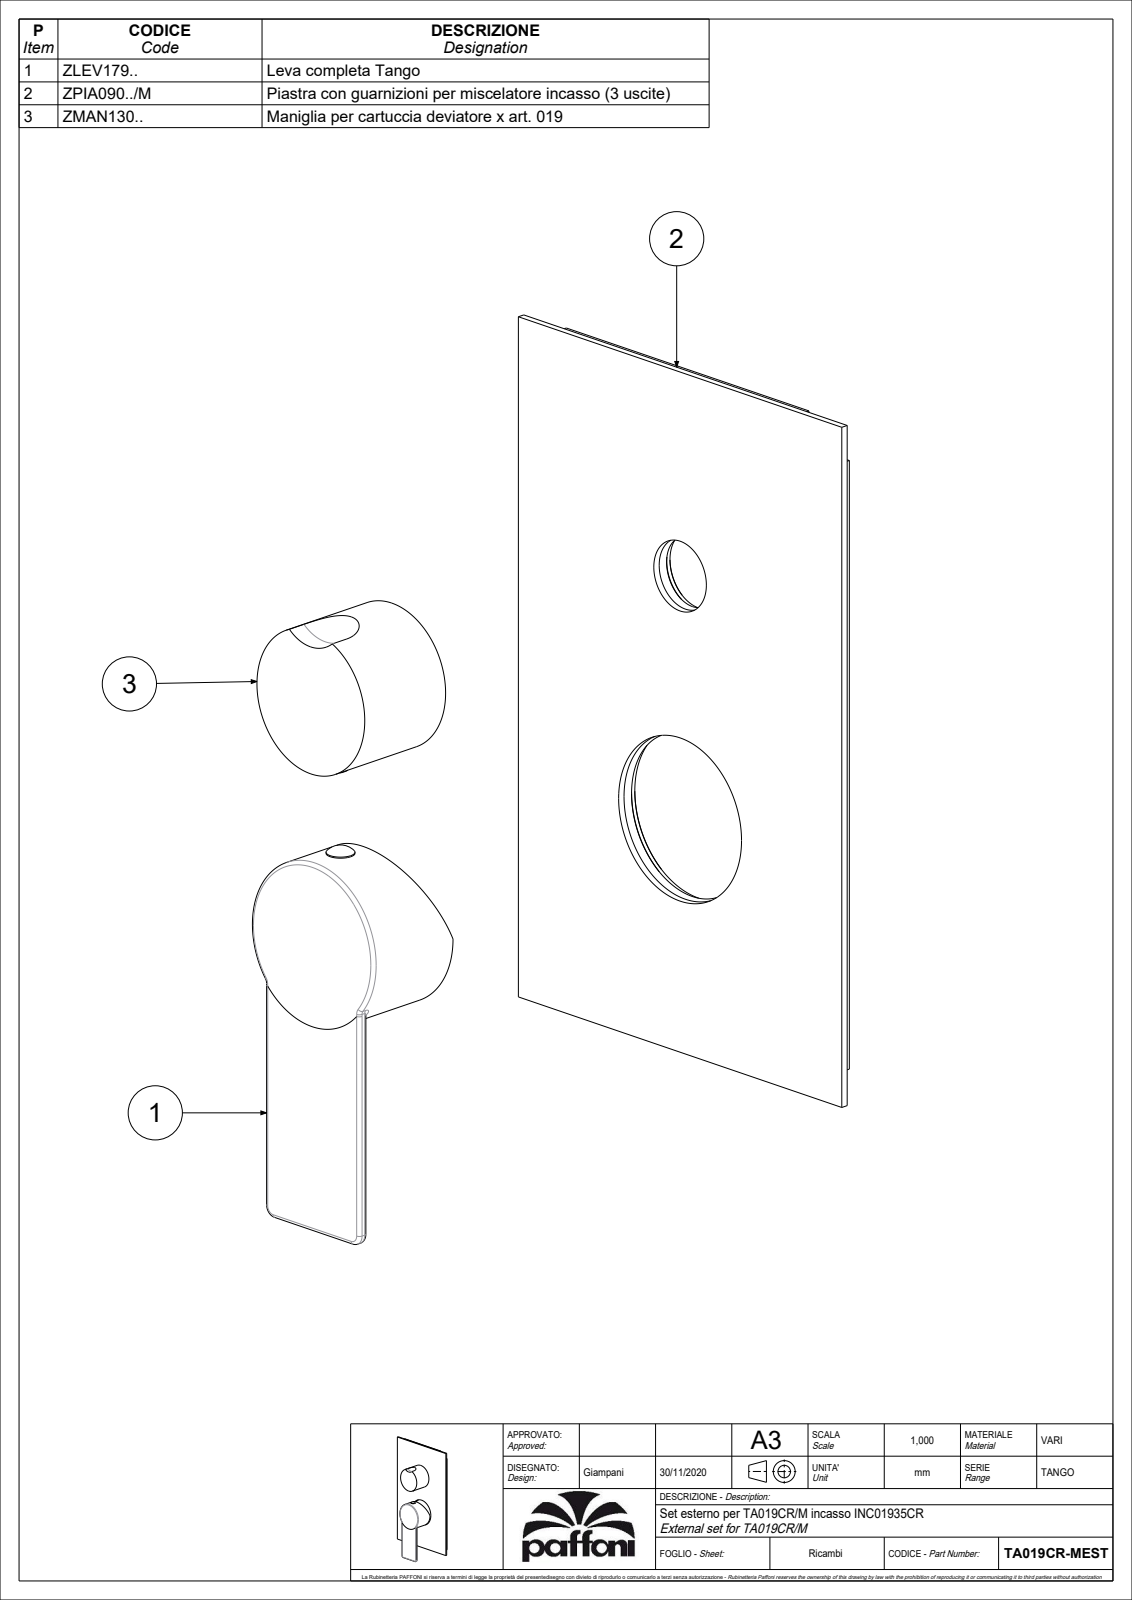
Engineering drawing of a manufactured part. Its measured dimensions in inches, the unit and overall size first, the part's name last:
Units: inches
Overall size (bounding box): 8.071 × 4.724 × 1.569
Round holes (diameter × count): ⌀0.118 ×2, ⌀0.126 ×1, ⌀0.165 ×1, ⌀0.583 ×1, ⌀0.768 ×1, ⌀0.846 ×1, ⌀0.984 ×1, ⌀1.417 ×1, ⌀1.795 ×1, ⌀1.874 ×1, ⌀2.012 ×1
Round bosses / shafts (diameter × count): ⌀0.299 ×2, ⌀0.217 ×2, ⌀2.15 ×1, ⌀1.791 ×1, ⌀1.575 ×1, ⌀1.122 ×1, ⌀0.945 ×1, ⌀0.197 ×1
Partial cylindrical surfaces — rounded edges, fillets, slot ends (radius × count): R0.039 ×6, R0.059 ×4, R0.02 ×2, R0.118 ×2, R0.138 ×1, R0.492 ×1
Main face-to-face distances: 0.079, 0.031, 0.11, 1.35, 0.118, 1.122, 1.319, 1.24, 1.201, 1.232
Hole centre spacings: 0.039, 0.394, 2.677, 3.071
Volume: 5.747 in³ · Surface area: 115.3 in²
Bodies: 3 solids, 243 faces (101 planar, 78 cylindrical, 64 other)
Part name (STEP PRODUCT): TA019CR-MEST
STEP written by: CREO PARAMETRIC BY PTC INC, 2020044 (CONFIG_CONTROL_DESIGN)
